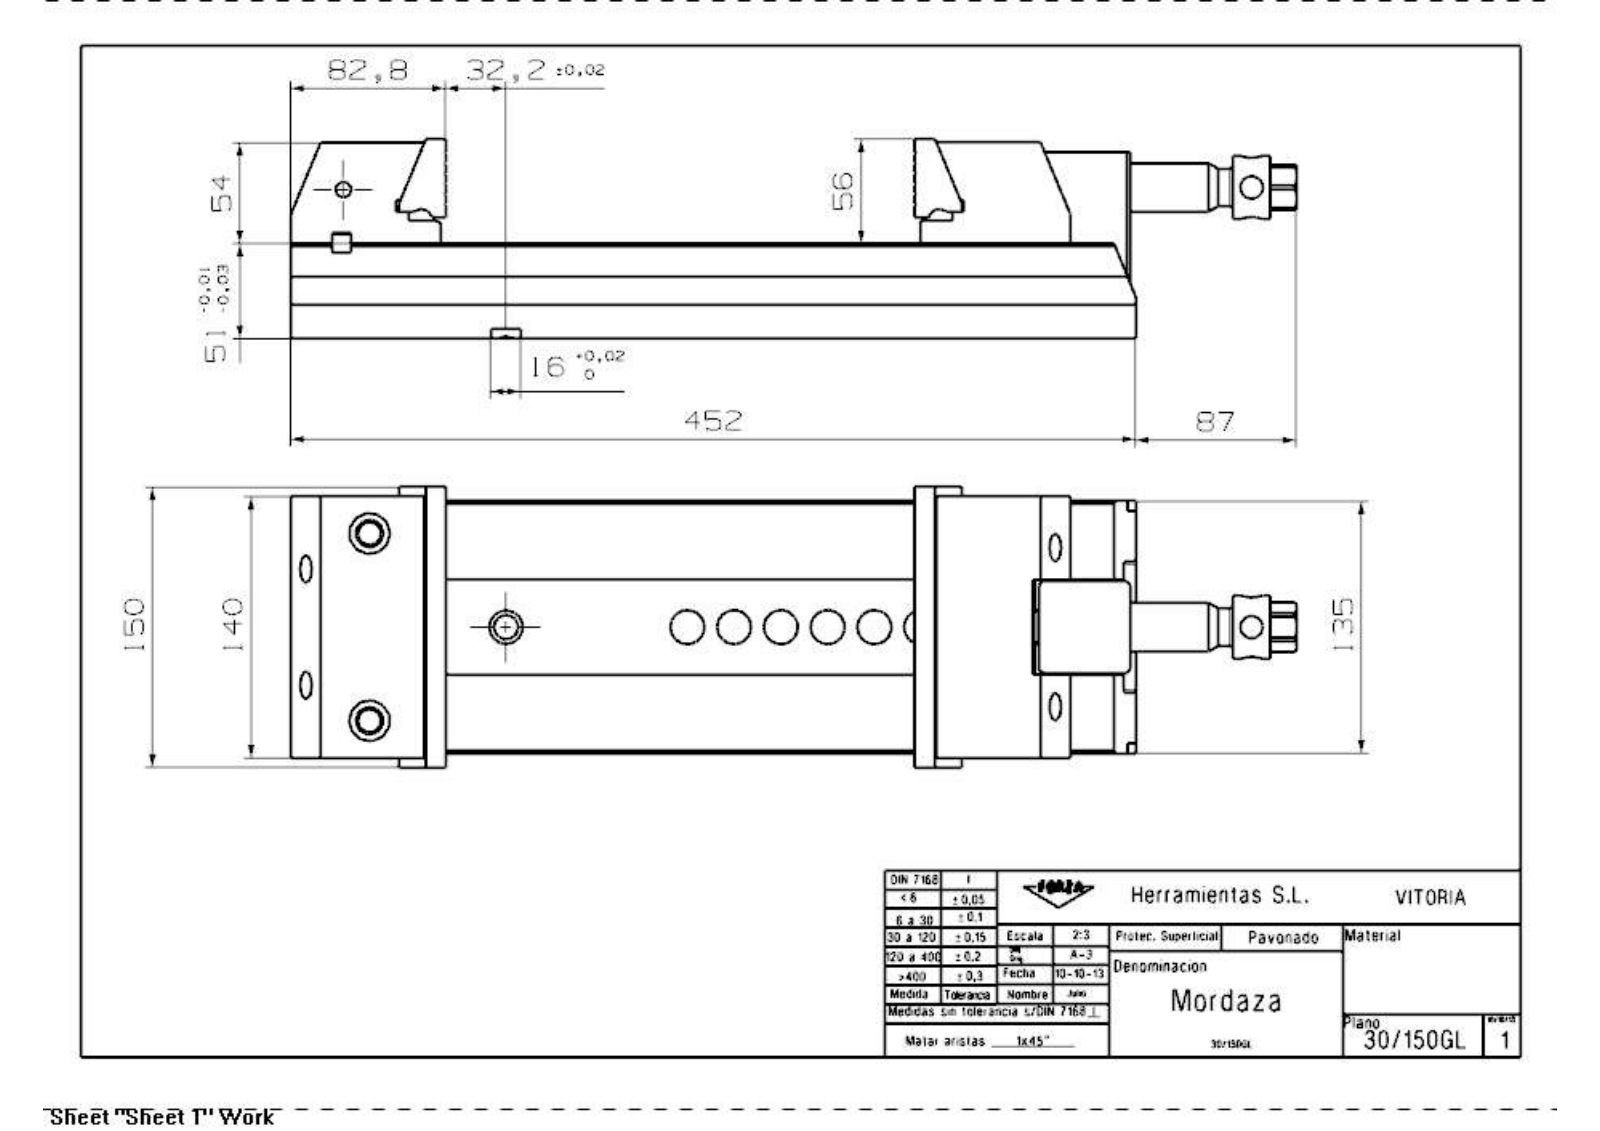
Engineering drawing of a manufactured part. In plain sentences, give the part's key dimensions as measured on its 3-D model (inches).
The part is named "30_150GL_Mordaza". Its 3-D file was written by "SIEMENS PLM Software NX 7.5 (AUTOMOTIVE_DESIGN)". It is 12 solids with 448 faces: 296 planar, 98 cylindrical and 54 other. Overall it measures 21.172 by 5.906 by 4.213 inches. Its volume is 208.4 cubic inches and its surface area 735.9 square inches. Round holes: 6 of diameter 0.512, 6 of diameter 0.591, 5 of diameter 0.204, 4 of diameter 0.275, 4 of diameter 0.335, 4 of diameter 0.346, 4 of diameter 0.417, 4 of diameter 0.748, 2 of diameter 0.382, 2 of diameter 0.394, 2 of diameter 0.472, 2 of diameter 0.487. Round bosses or shafts: 1 of diameter 1.339, 1 of diameter 1.331, 1 of diameter 1.024, 1 of diameter 0.787, 1 of diameter 0.65. Partial cylindrical surfaces (rounded edges, fillets, slot ends): 4 of radius 0.059, 4 of radius 0.315, 4 of radius 0.787, 2 of radius 0.063, 2 of radius 0.217, 2 of radius 0.236, 1 of radius 0.157, 1 of radius 0.354. The main face-to-face distances are 2.008, 0.76, 1.248, 0.217, 1.945, 0.315, 1.378, 0.063, 0.697, 2.136. The hole center spacings are 0.453, 2.894, 2.441, 2.648, 3.346, 3.295, 3.295, 3.747.
